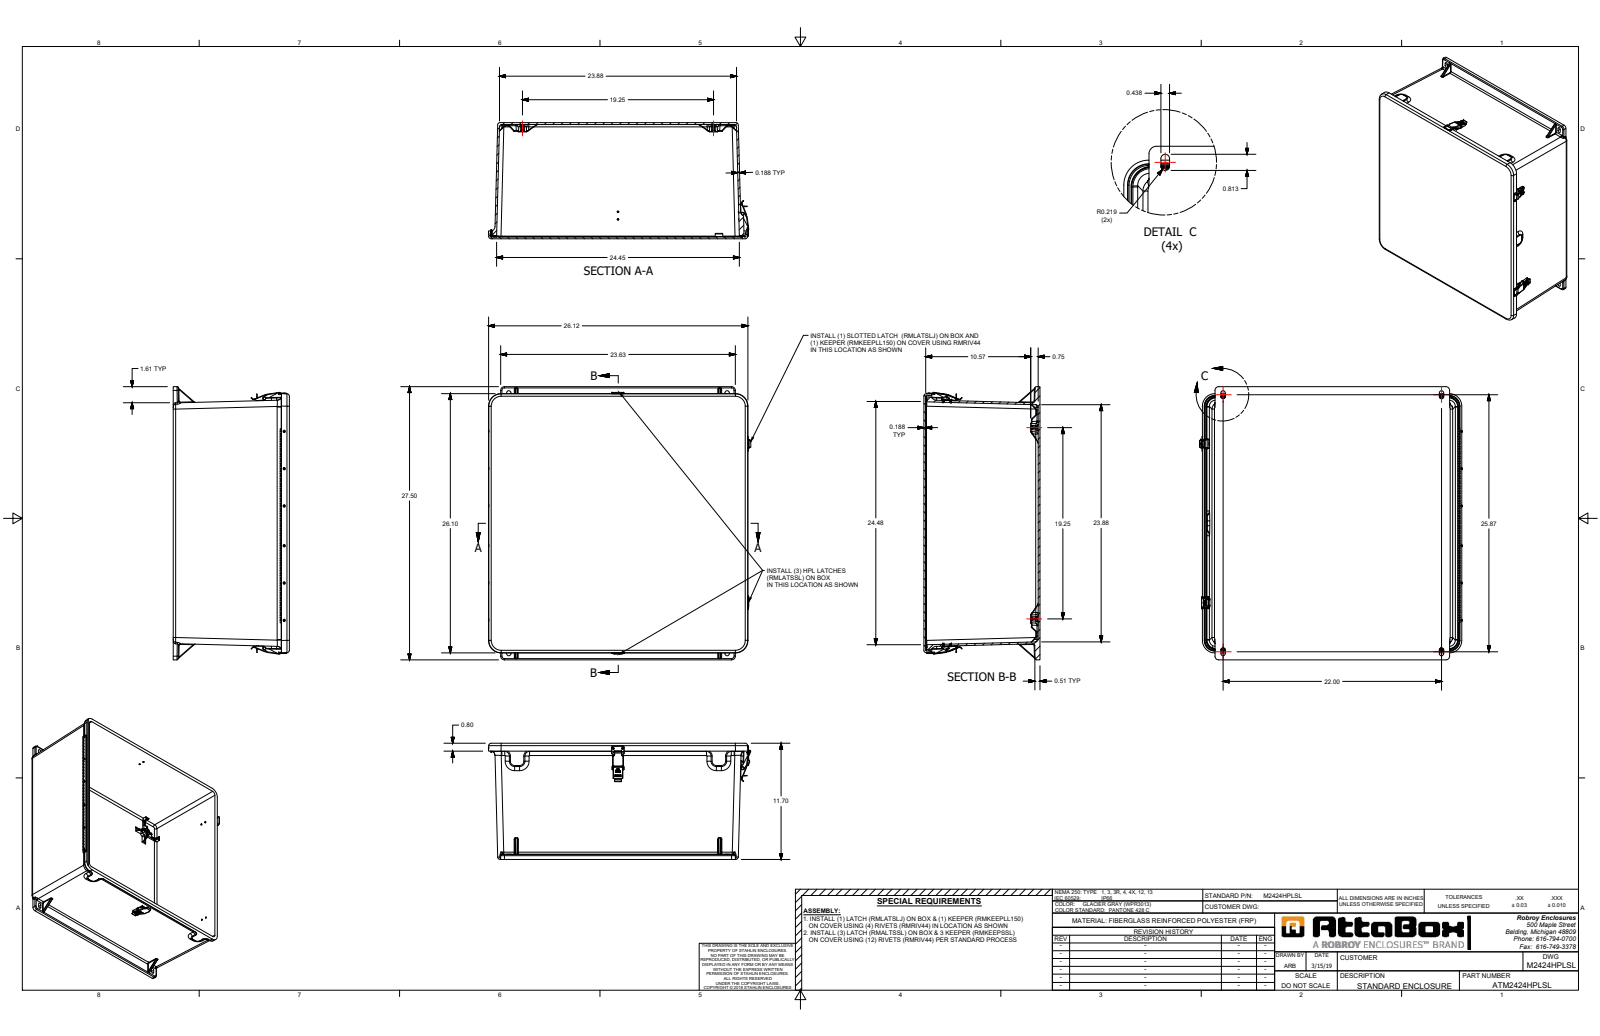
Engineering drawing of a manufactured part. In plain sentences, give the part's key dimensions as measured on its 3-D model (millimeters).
The part is named "M2424HPLSL". Its 3-D file was written by "SolidWorks 2019 (AUTOMOTIVE_DESIGN)". It is 60 solids with 3818 faces: 1469 planar, 1057 cylindrical and 1292 other. Overall it measures 698.5 by 670.2 by 297.2 millimeters. Its volume is 8 654 000 cubic millimeters and its surface area 3 412 000 square millimeters. Round holes: 26 of diameter 2.6, 24 of diameter 3.5, 12 of diameter 3.3, 6 of diameter 3.3, 6 of diameter 3.4, 6 of diameter 3.4, 6 of diameter 3.6, 4 of diameter 5.2, 4 of diameter 9.9, 3 of diameter 9.5, 2 of diameter 3.3, 2 of diameter 3.4. Round bosses or shafts: 10 of diameter 3.2, 8 of diameter 3.6, 8 of diameter 3.2, 3 of diameter 7.6, 3 of diameter 4.3, 3 of diameter 3, 1 of diameter 15.1, 1 of diameter 13.3. Partial cylindrical surfaces (rounded edges, fillets, slot ends): 78 of radius 1.5, 72 of radius 0.1, 44 of radius 3.2, 39 of radius 6.4, 36 of radius 0.4, 35 of radius 0.5, 33 of radius 1.5, 24 of radius 1.1. The main face-to-face distances are 4.8, 292.4, 4.8, 297.1, 287.6, 641.7, 7.3, 12, 1.9, 6.6. The hole center spacings are 95.4, 23.8, 95.3, 292.4, 95.3, 184.3, 190.7, 197.1.
